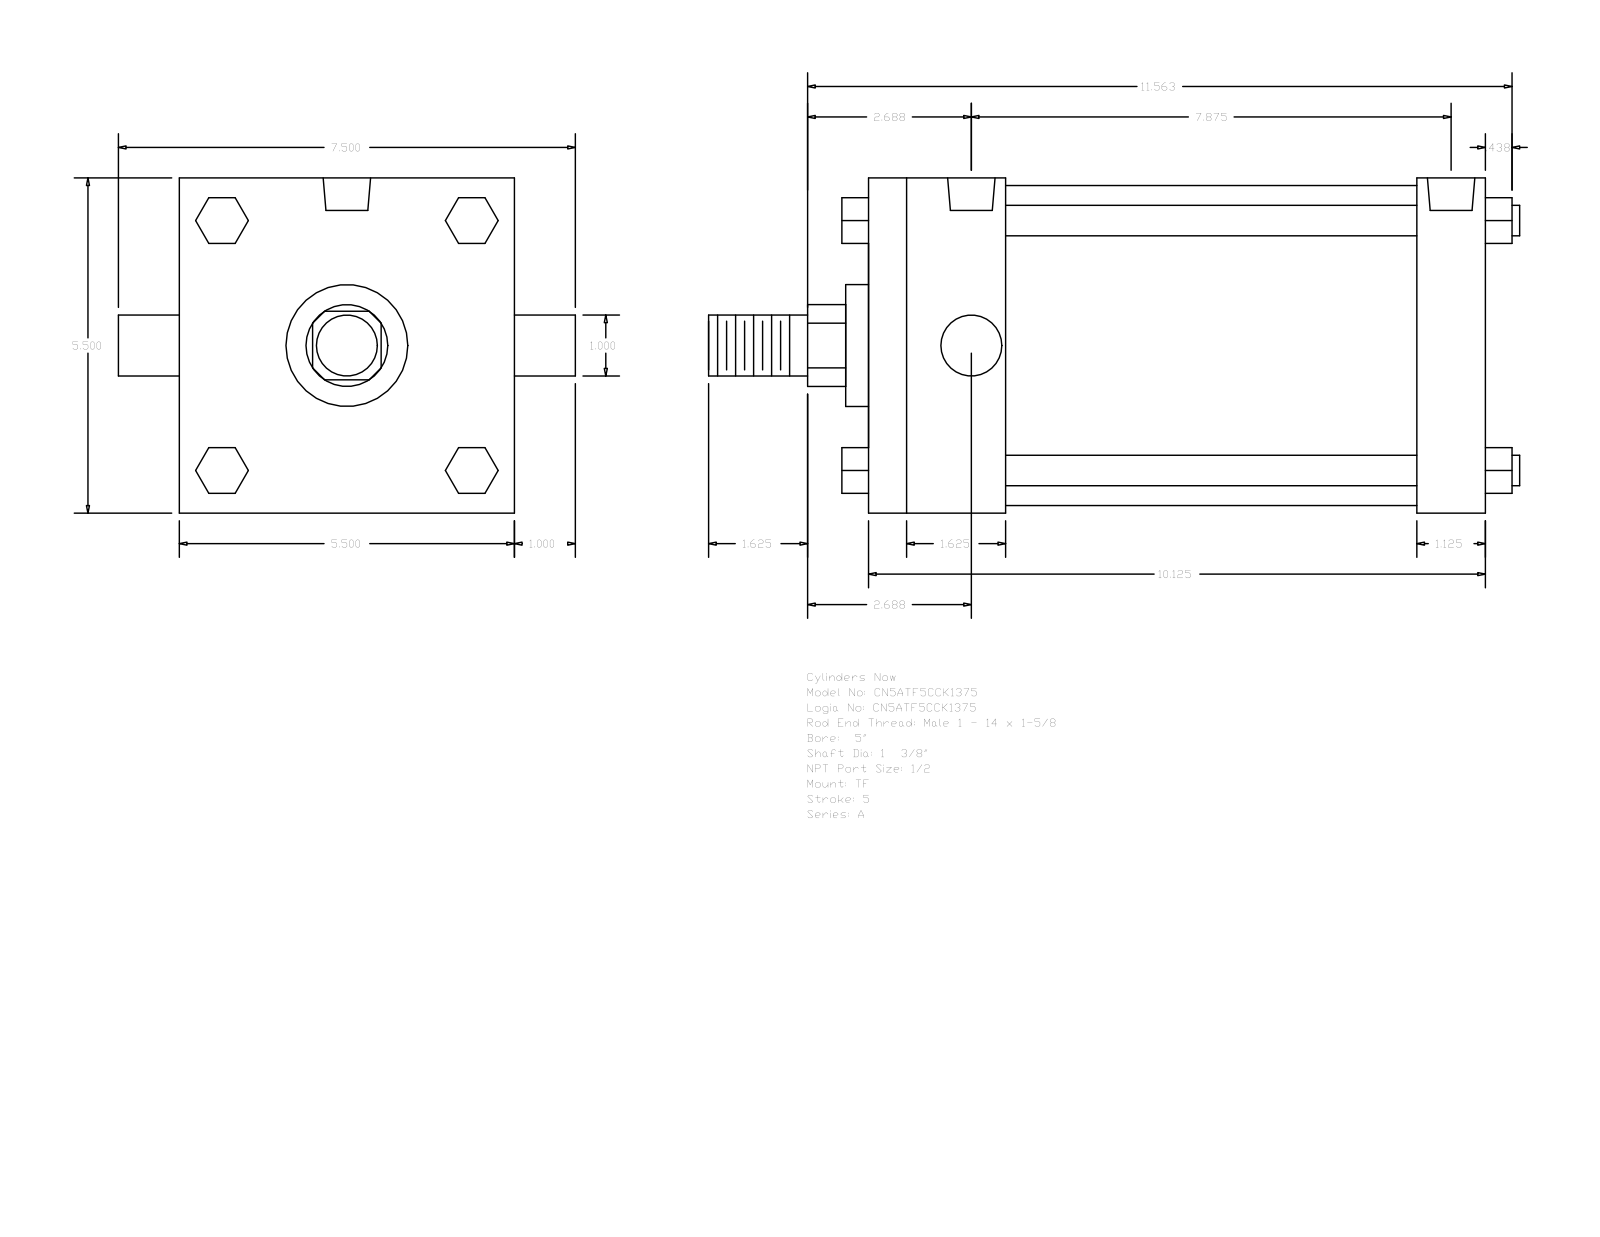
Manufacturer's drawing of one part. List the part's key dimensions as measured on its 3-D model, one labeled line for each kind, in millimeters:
Part name (STEP PRODUCT): A_TF__0500_1.375
STEP written by: GSSL Pune (CONFIG_CONTROL_DESIGN)
Units: millimetres
Bodies: 0 solids, 120 faces (92 planar, 28 cylindrical, 0 other)
Overall size (bounding box): 338.14 × 190.5 × 139.7
Round holes (diameter × count): ⌀8.73 ×3, ⌀19.77 ×2
Round bosses / shafts (diameter × count): ⌀12.7 ×4, ⌀25.4 ×2, ⌀133.35 ×1, ⌀50.8 ×1, ⌀34.92 ×1
Partial cylindrical surfaces — rounded edges, fillets, slot ends (radius × count): R17.06 ×1
Main face-to-face distances: 139.7, 257.17, 57.15, 228.6, 28.57, 171.45, 200.02, 19.05, 52.07, 90.18
Hole centre spacings: 2.39, 197.64, 195.25, 200.03
